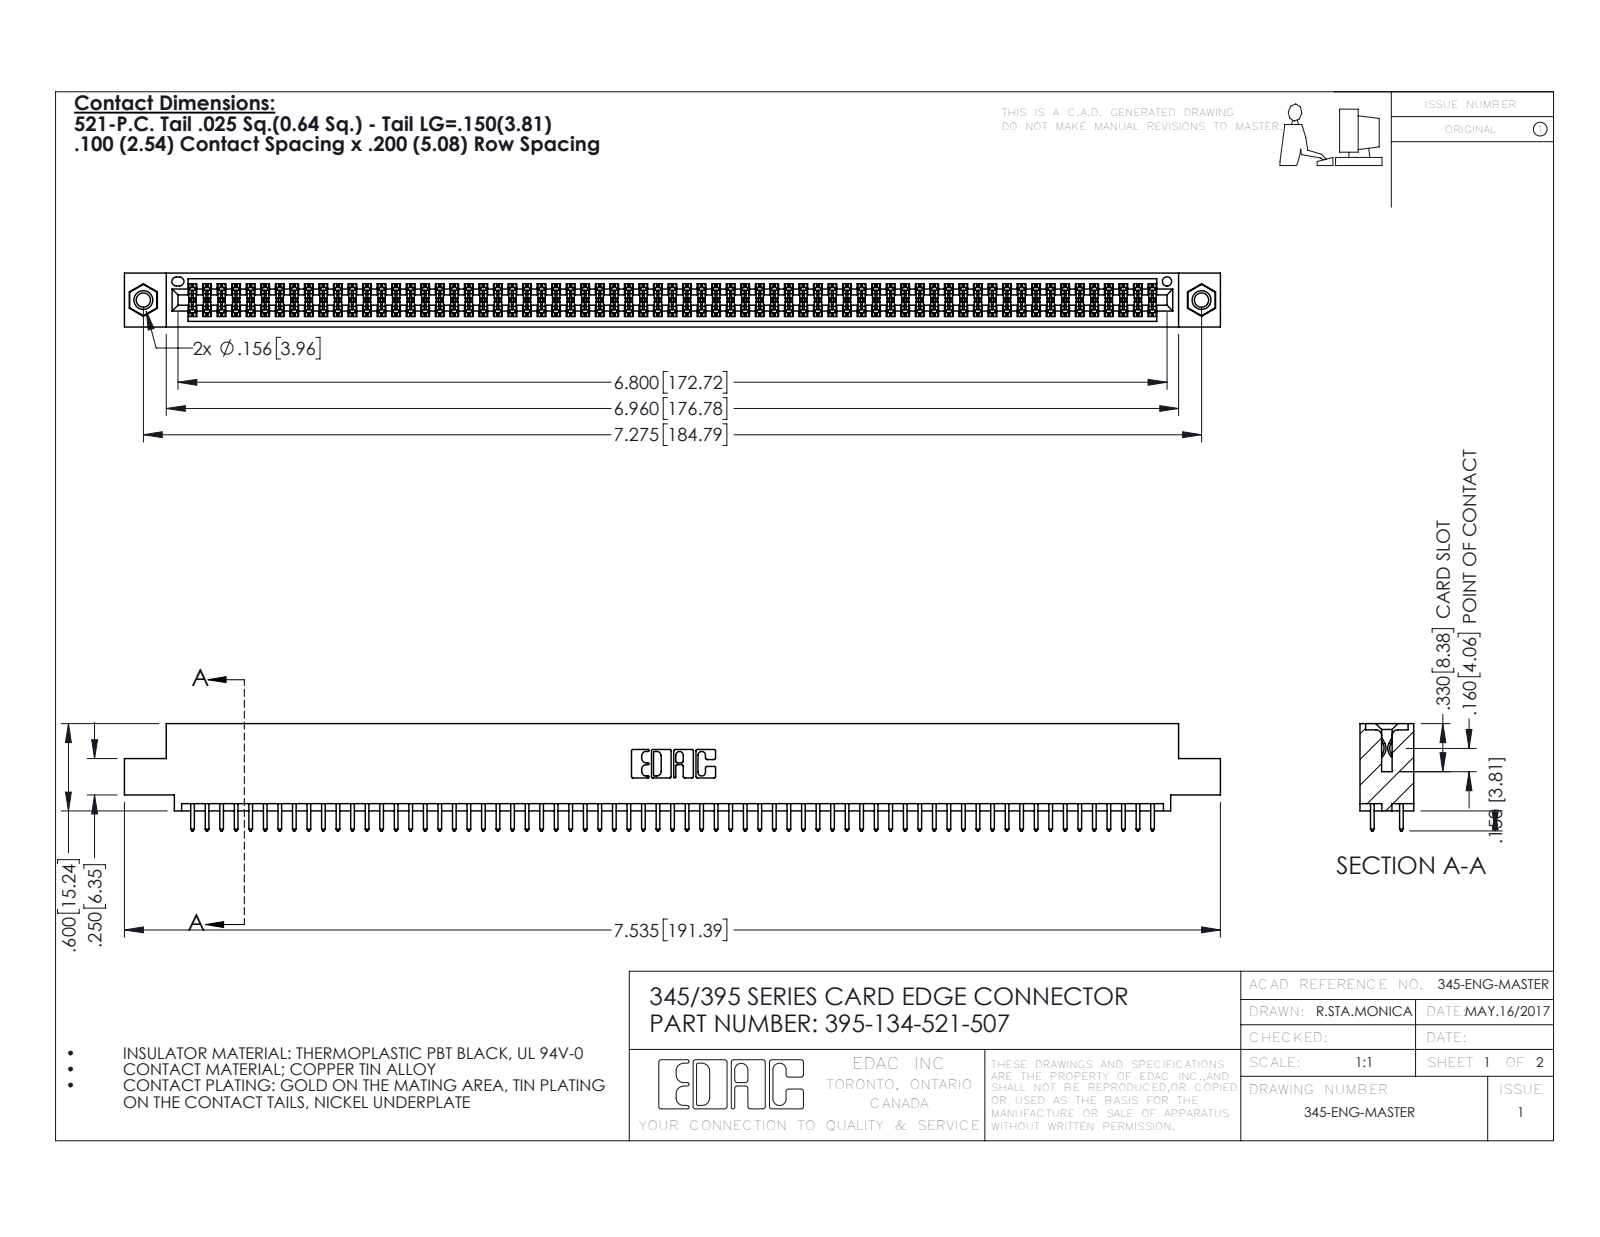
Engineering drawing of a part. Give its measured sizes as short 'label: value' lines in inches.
name: 395-134-521-507; 345 Part_0.110 Offset - 0.156 Dia-TI; 345-250-001_345-250-005-103; 345-292-001_345-293-121
written by: SolidWorks 2016 (CONFIG_CONTROL_DESIGN)
unit: in
bodies: 137 solids, 6890 faces (4538 planar, 2336 cylindrical, 16 other)
size: 7.535 × 0.737 × 0.37
volume: 1.14 in³; area: 43.19 in²
holes: 2× ⌀0.098, 2× ⌀0.125, 2× ⌀0.156, 1× ⌀0.064
bosses: 2× ⌀0.155
rounds: 201× R0.006, 134× R0.01, 22× R0.01, 6× R0.007, 6× R0.031, 3× R0.026, 2× R0.014, 2× R0.019
face distances: 0.072, 0.298, 0.2, 0.098, 0.272, 0.025, 0.37, 0.225, 0.175, 0.149
hole spacings: 0.27, 7.039, 7.275
